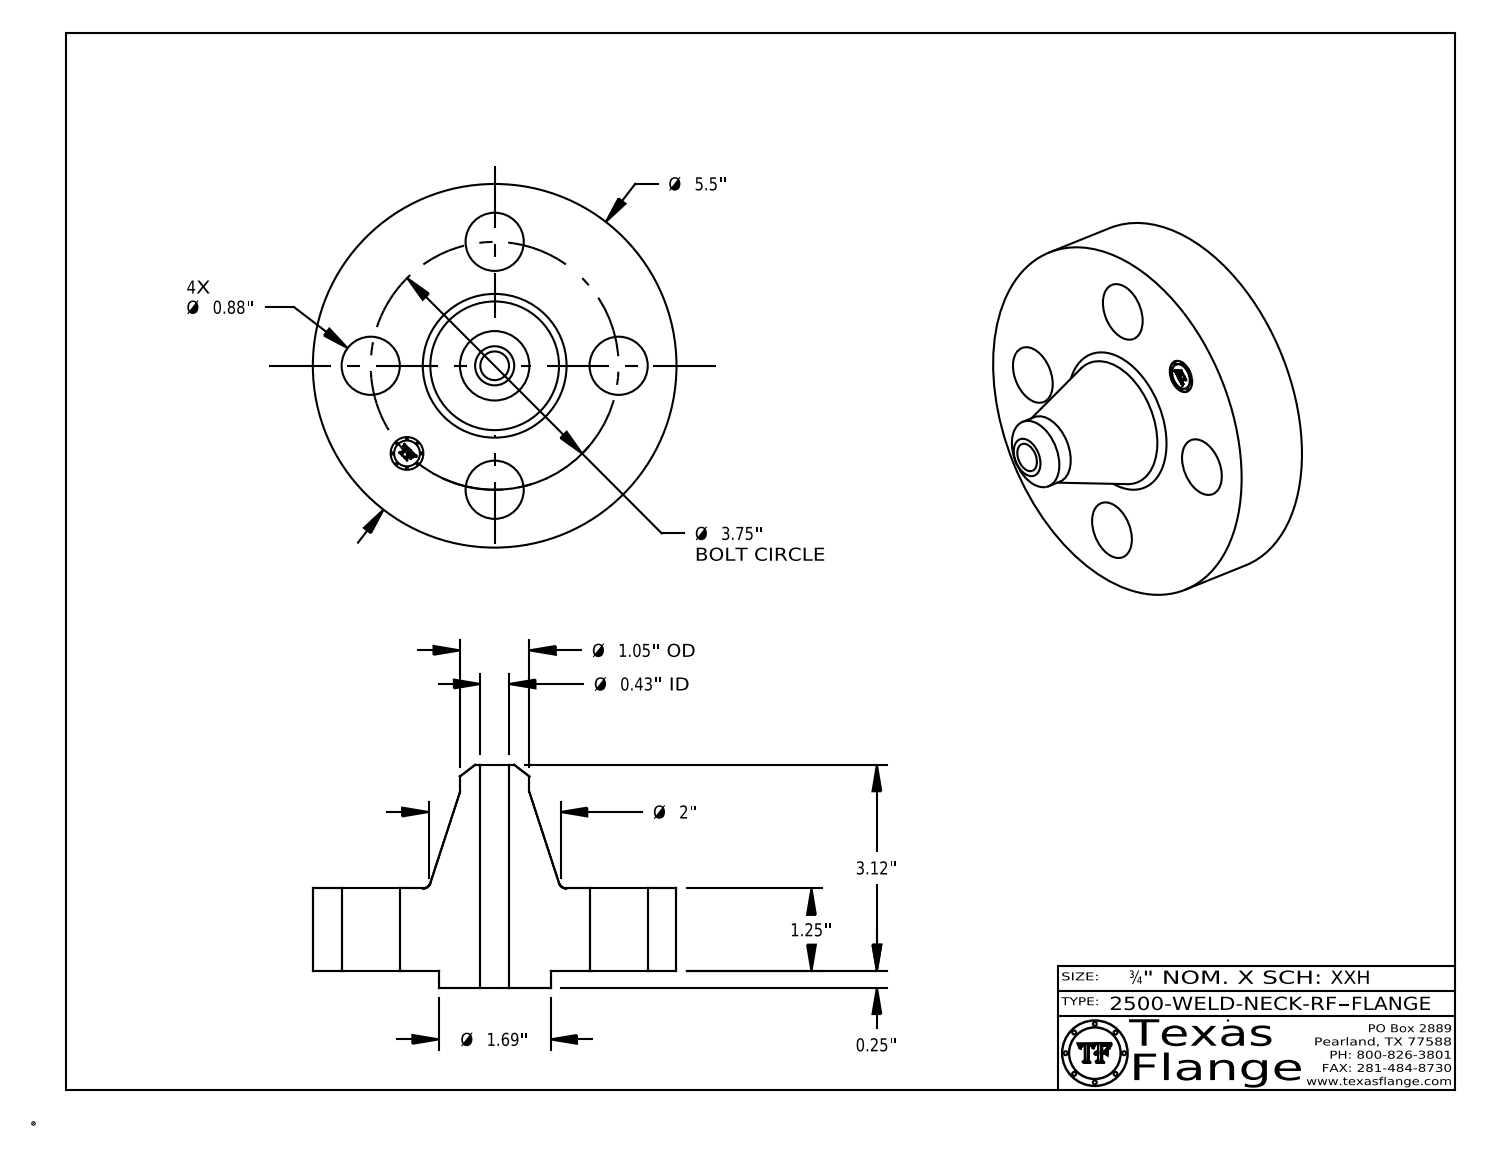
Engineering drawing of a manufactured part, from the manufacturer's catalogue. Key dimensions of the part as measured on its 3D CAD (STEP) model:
Part name (STEP PRODUCT): 2500-WELD-NECK-RF
STEP written by: CATIA V5 STEP AP214 (AUTOMOTIVE_DESIGN)
Units: inches
Bodies: 1 solid, 411 faces (369 planar, 36 cylindrical, 6 other)
Overall size (bounding box): 5.5 × 5.5 × 3.37
Volume: 29.78 in³ · Surface area: 89.65 in²
Round holes (diameter × count): ⌀0.88 ×4, ⌀0.434 ×1, ⌀0.495 ×1
Round bosses / shafts (diameter × count): ⌀0.03 ×8, ⌀5.5 ×1, ⌀1.69 ×1, ⌀1.05 ×1, ⌀0.39 ×1
Main face-to-face distances: 1.25, 0.25, 1.5, 3.37, 3.12, 1.87, 1.485, 1.235, 0.015, 1.885
Hole centre spacings: 1.875, 2.652, 1.435, 3.465, 3.75
